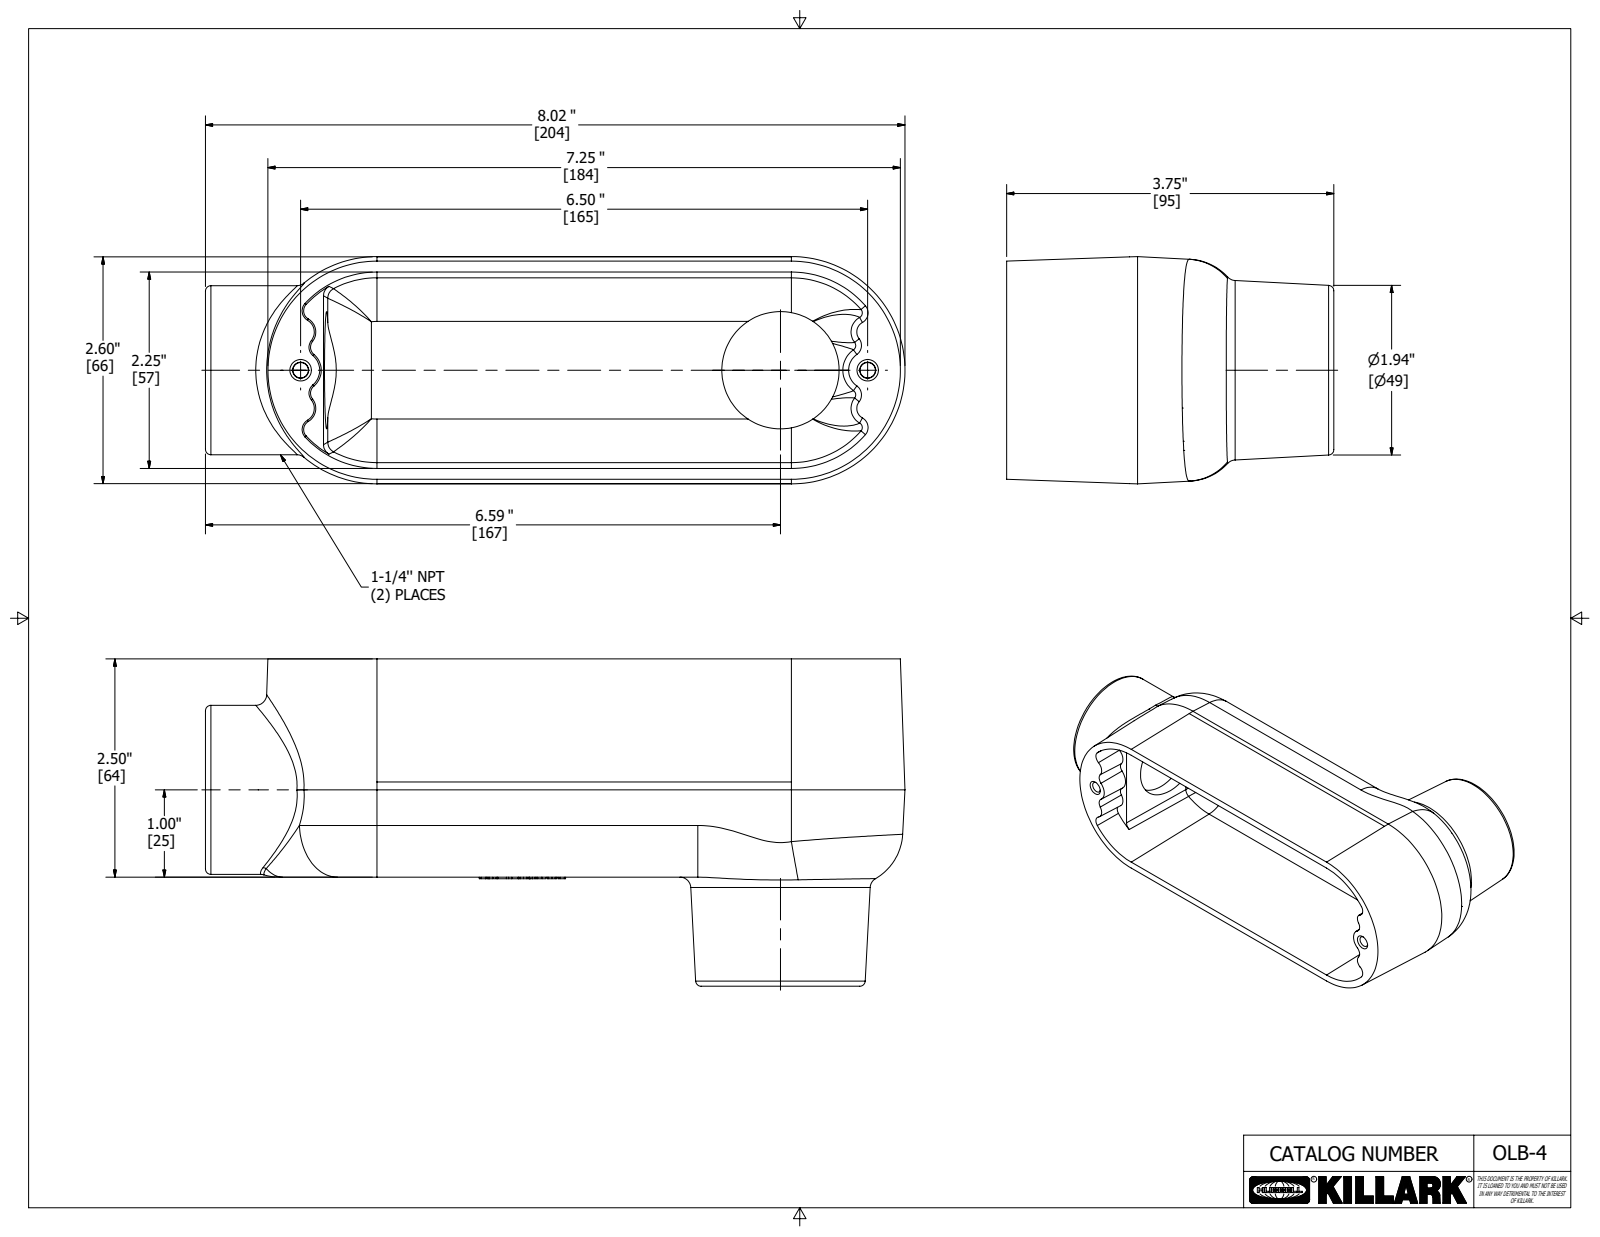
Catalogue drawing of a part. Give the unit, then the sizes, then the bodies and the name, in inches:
Units: inches
Overall size (bounding box): 8.018 × 3.75 × 2.605
Round holes (diameter × count): ⌀1.344 ×2
Round bosses / shafts (diameter × count): ⌀1.937 ×1
Partial cylindrical surfaces — rounded edges, fillets, slot ends (radius × count): R0.5 ×3, R0.625 ×2
Main face-to-face distances: 2.373, 0.125, 2.5, 2.375, 0.031, 0.156, 2.344, 0.094, 2.469, 0.094
Volume: 13.36 in³ · Surface area: 127.3 in²
Bodies: 1 solid, 345 faces (157 planar, 8 cylindrical, 180 other)
Part name (STEP PRODUCT): 17173-1
STEP written by: Autodesk Inventor 2018 (AUTOMOTIVE_DESIGN)
